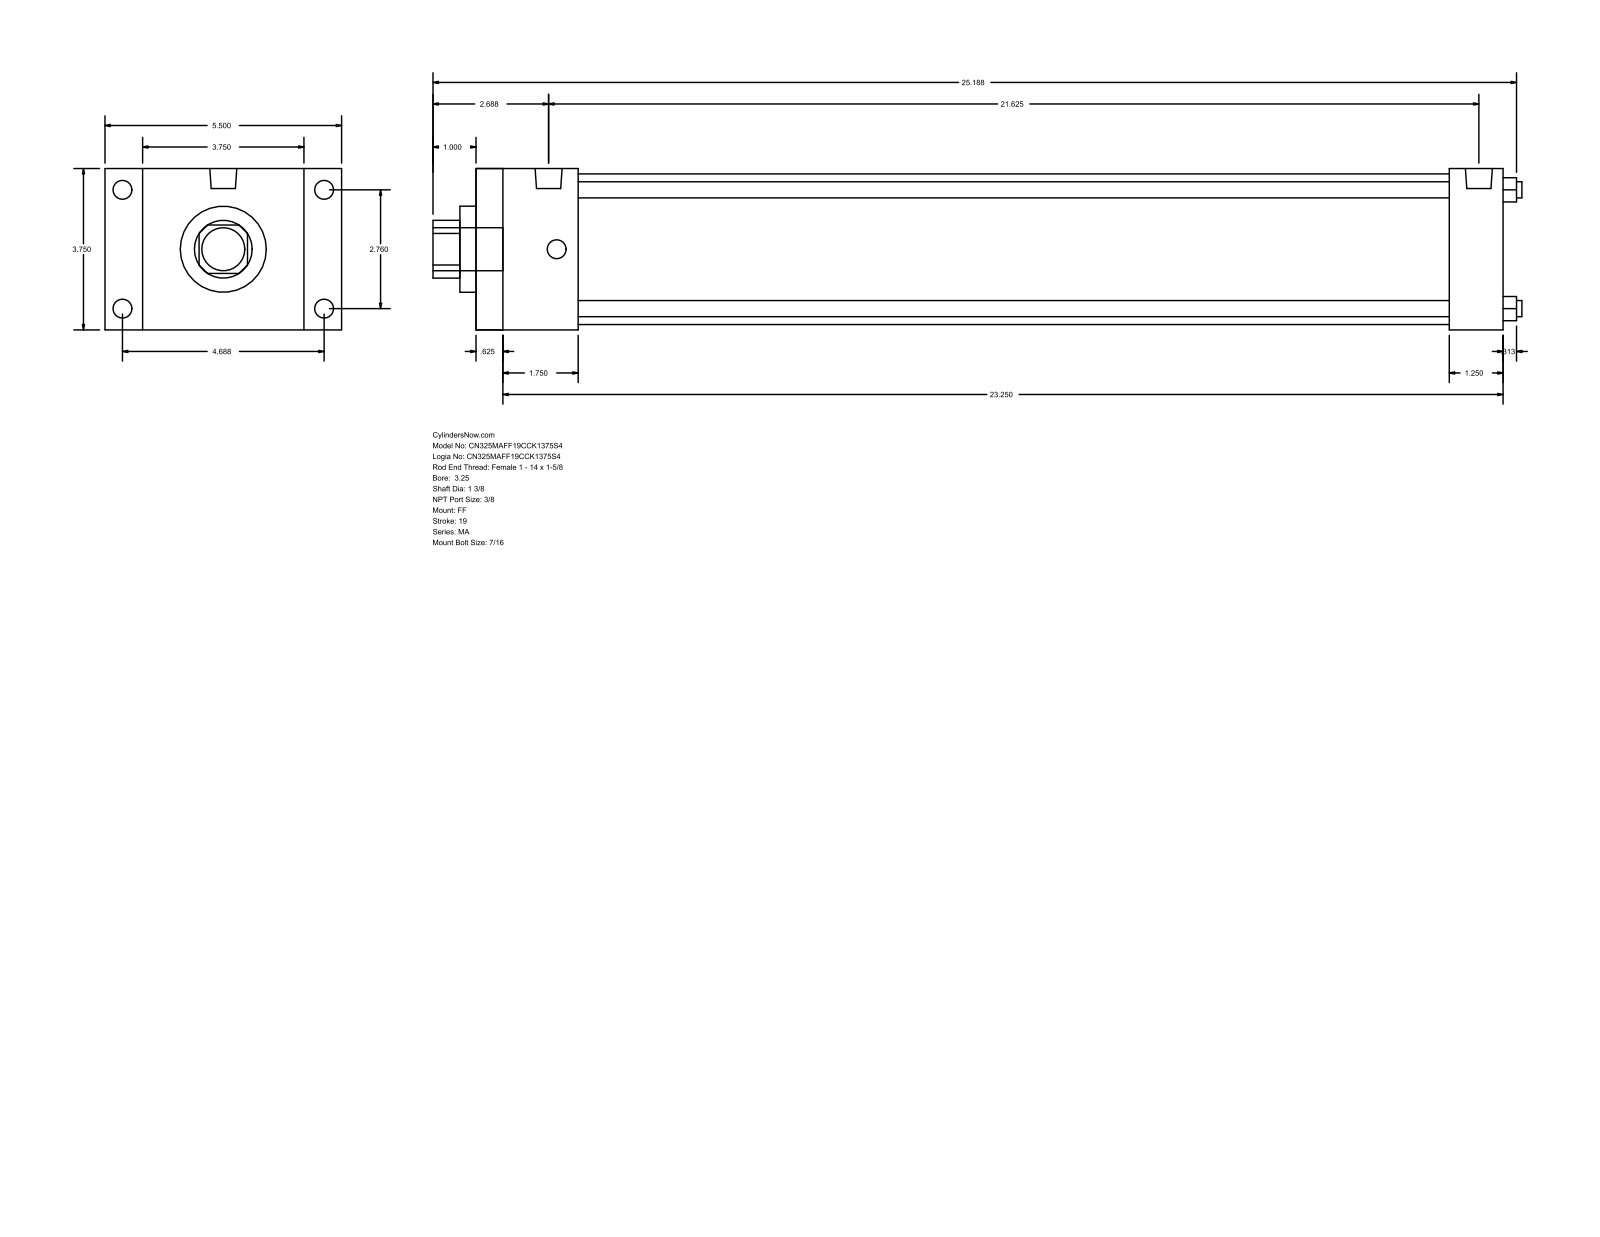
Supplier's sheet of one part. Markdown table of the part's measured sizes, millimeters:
| quantity | value |
| --- | --- |
| part name | MA_FF__0325_1.375 |
| STEP written by | GSSL Pune (CONFIG_CONTROL_DESIGN) |
| units | millimeters |
| bodies | 0 solids, 92 faces (64 planar, 28 cylindrical, 0 other) |
| overall size | 642.94 × 139.7 × 95.25 |
| round holes (diameter × count) | 9.53 × 4, 34.92 × 1, 50.8 × 1, 88.9 × 1 |
| round bosses / shafts (diameter × count) | 11.11 × 8, 15.93 × 2, 25.4 × 1 |
| partial cylindrical surfaces (radius × count) | 17.06 × 1 |
| main face-to-face distances | 95.24, 606.43, 15.87, 590.56, 22.23, 117.47, 60.32, 574.68, 44.45, 558.81 |
| hole center spacings | 49.57, 70.1, 99.14 |
